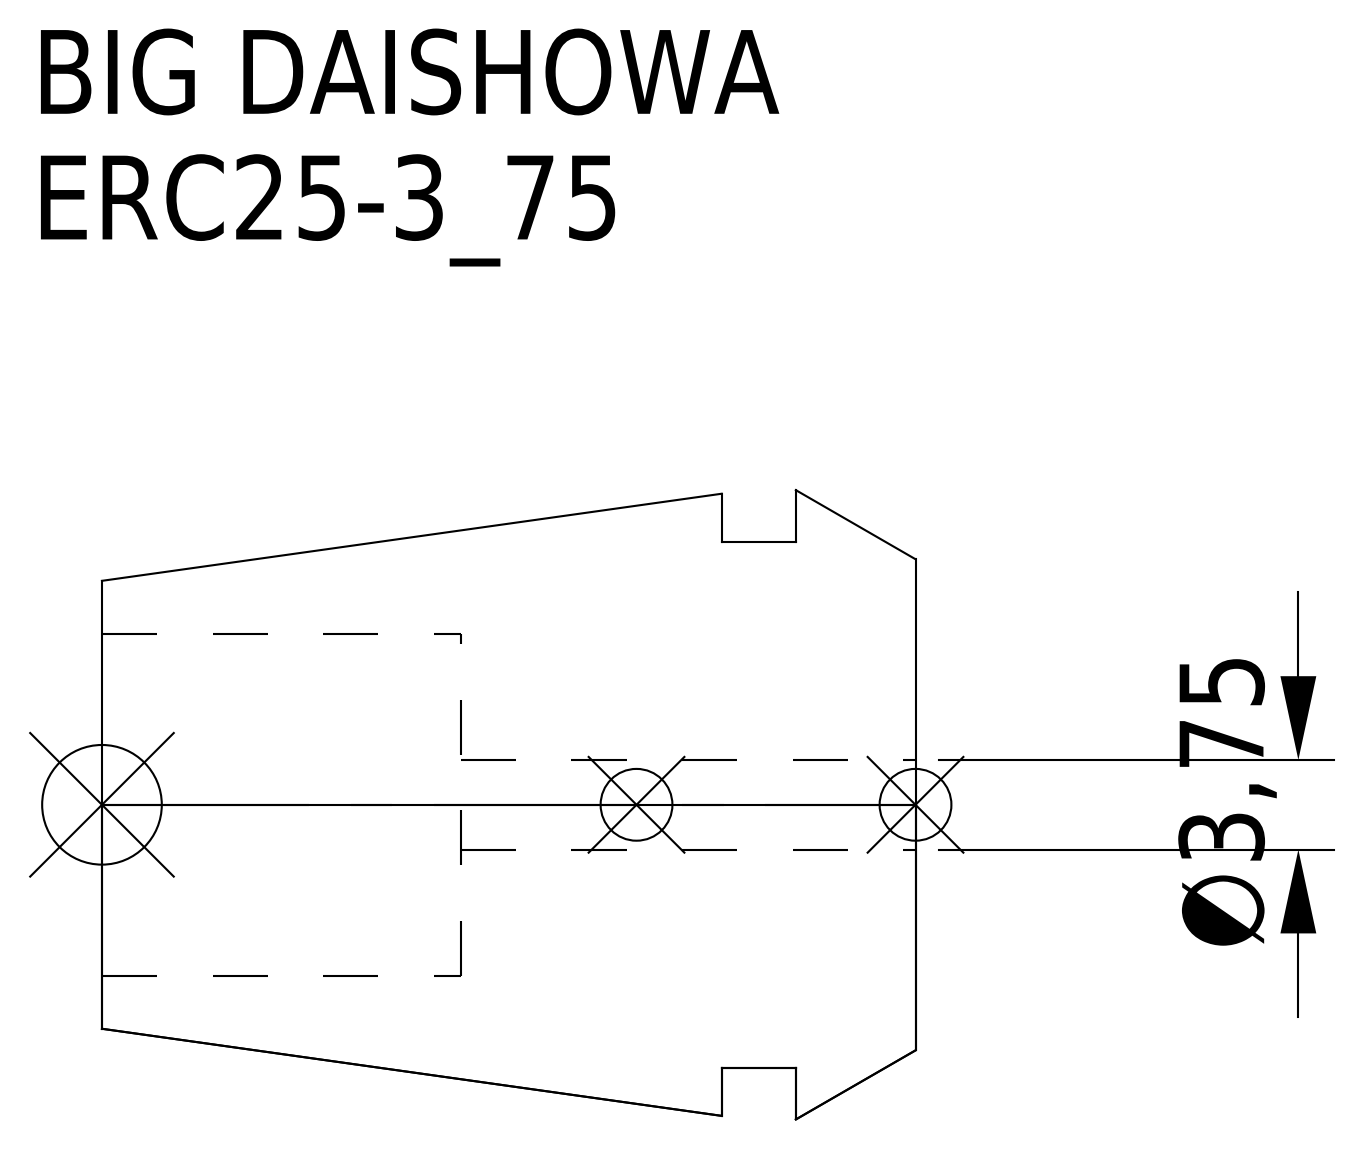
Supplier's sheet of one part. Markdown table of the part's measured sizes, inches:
| quantity | value |
| --- | --- |
| part name | ERC25-3_75 |
| STEP written by | CREO PARAMETRIC BY PTC INC, 2016380 (AUTOMOTIVE_DESIGN) |
| units | inches |
| bodies | 1 solid, 15 faces (5 planar, 6 cylindrical, 4 other) |
| overall size | 1.339 × 1.035 × 1.035 |
| volume | 0.67 in³ |
| surface area | 6.622 in² |
| round holes (diameter × count) | 0.148 × 1, 0.563 × 1 |
| round bosses / shafts (diameter × count) | 0.866 × 1 |
| main face-to-face distances | 0.197, 0.319, 0.122, 0.748, 0.551, 0.429, 1.339, 1.142, 1.02, 0.591 |
